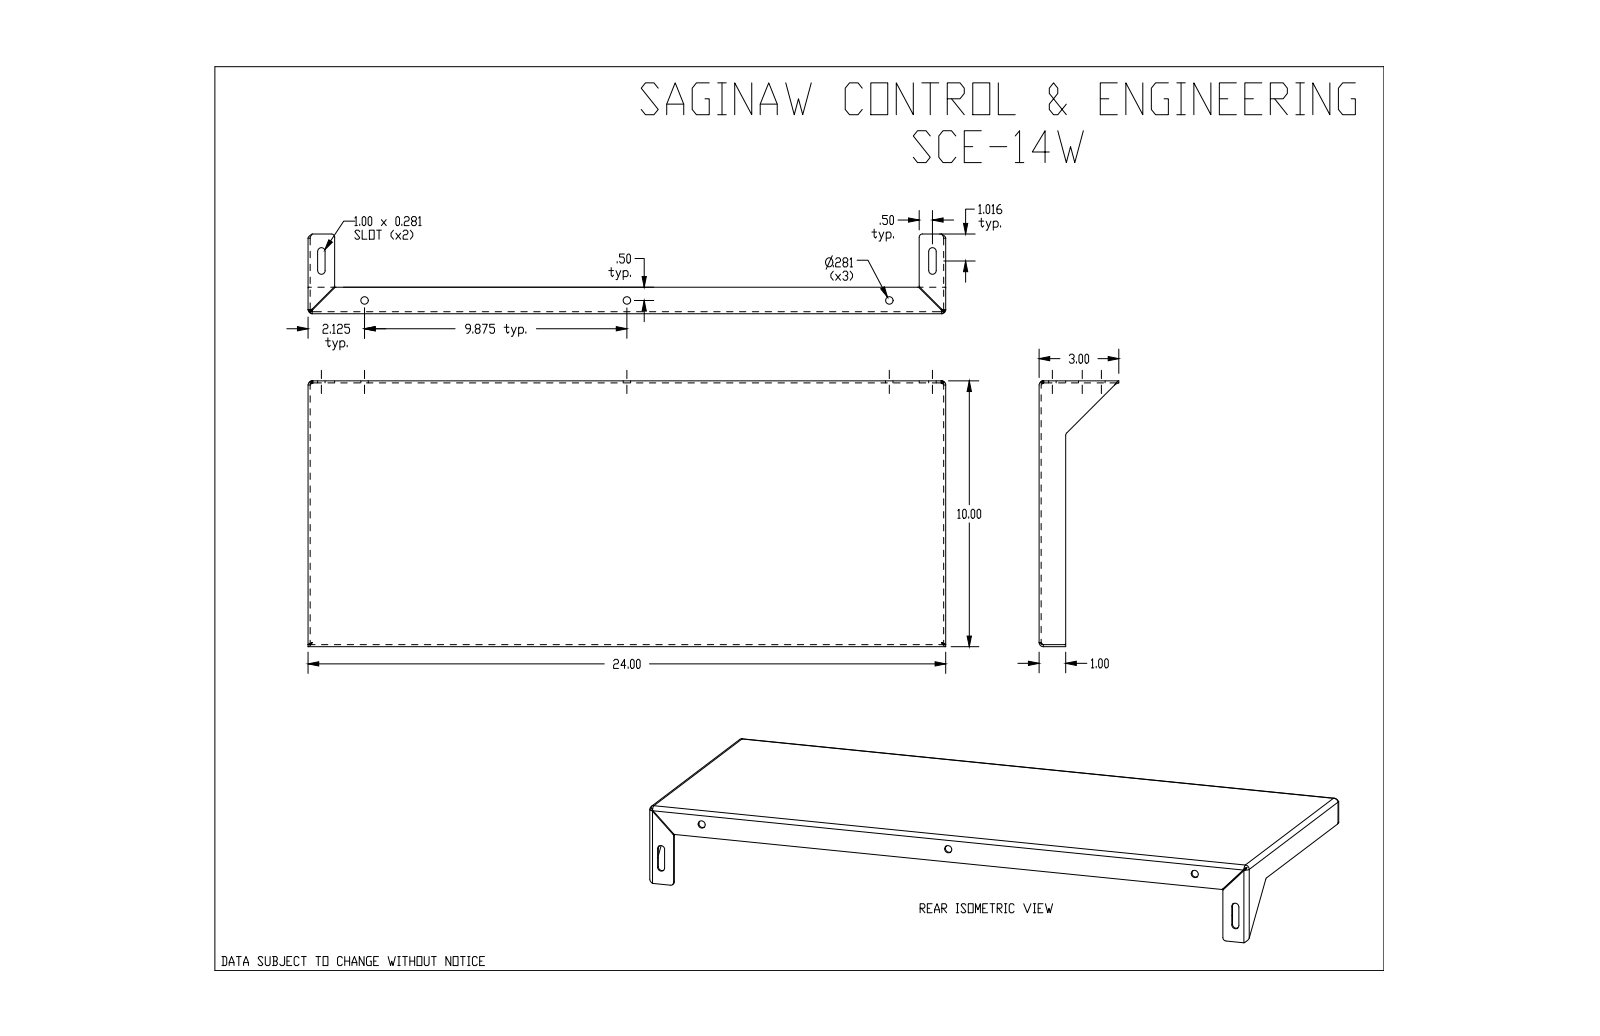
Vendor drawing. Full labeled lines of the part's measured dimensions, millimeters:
Part name (STEP PRODUCT): SCE-14W
STEP written by: SolidWorks 2019 (AUTOMOTIVE_DESIGN)
Units: millimetres
Bodies: 1 solid, 43 faces (28 planar, 13 cylindrical, 2 other)
Overall size (bounding box): 609.6 × 254 × 76.2
Volume: 253 300 mm³ · Surface area: 401 500 mm²
Round holes (diameter × count): ⌀7.1 ×3
Partial cylindrical surfaces — rounded edges, fillets, slot ends (radius × count): R3.6 ×4, R2.7 ×2, R4 ×2, R3.2 ×1
Main face-to-face distances: 1.3, 252.7, 608.3, 254, 251.5, 609.6, 607.1, 24.1, 25.4, 252.5
Hole centre spacings: 250.8, 250.8, 501.7
